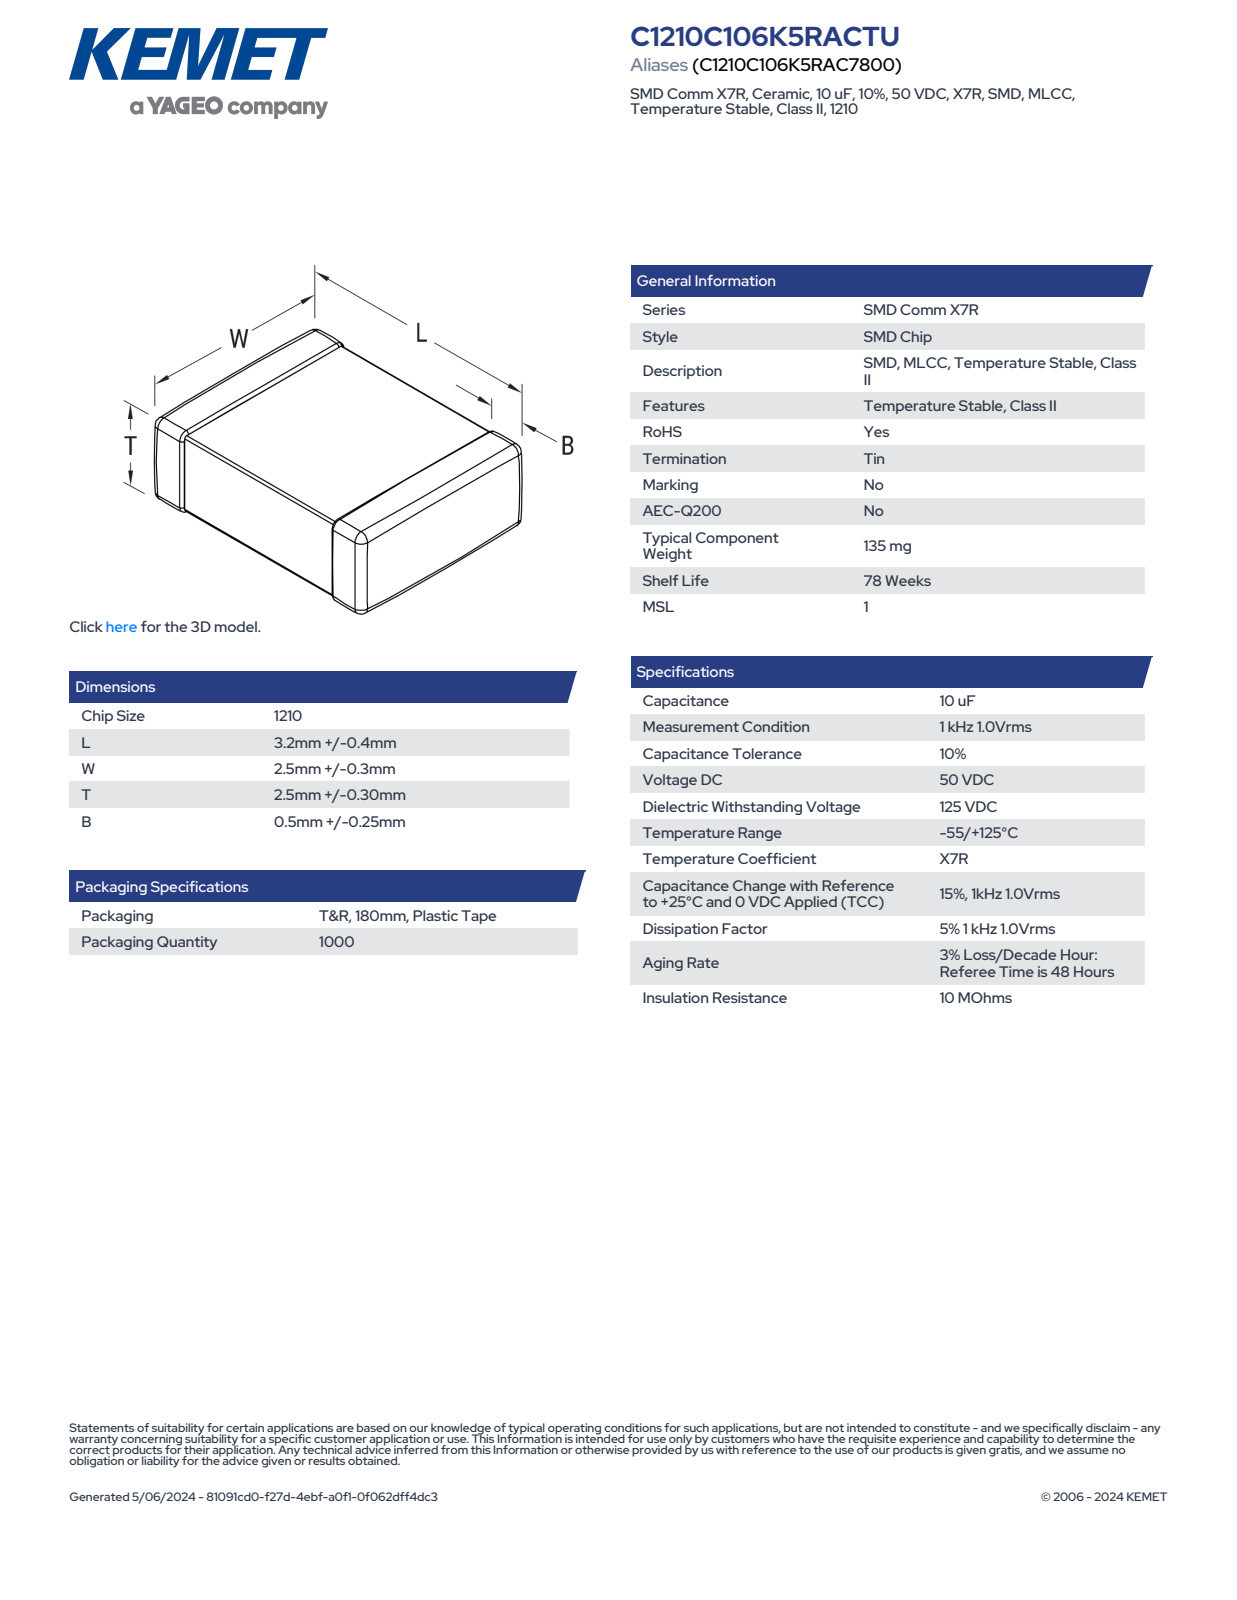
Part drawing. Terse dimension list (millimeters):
name: CCS_CCSTDNOS_1210_L3.6W2.8T2.8B0.75
written by: SolidWorks 2021 (AUTOMOTIVE_DESIGN)
unit: mm
bodies: 4 solids, 125 faces (71 planar, 38 cylindrical, 16 other)
size: 3.6 × 2.8 × 2.8
volume: 27 mm³; area: 55 mm²
face distances: 2.74, 2.68, 3.6, 2.8, 2.75, 2.69, 1.35, 1.45, 1.29, 1.39
